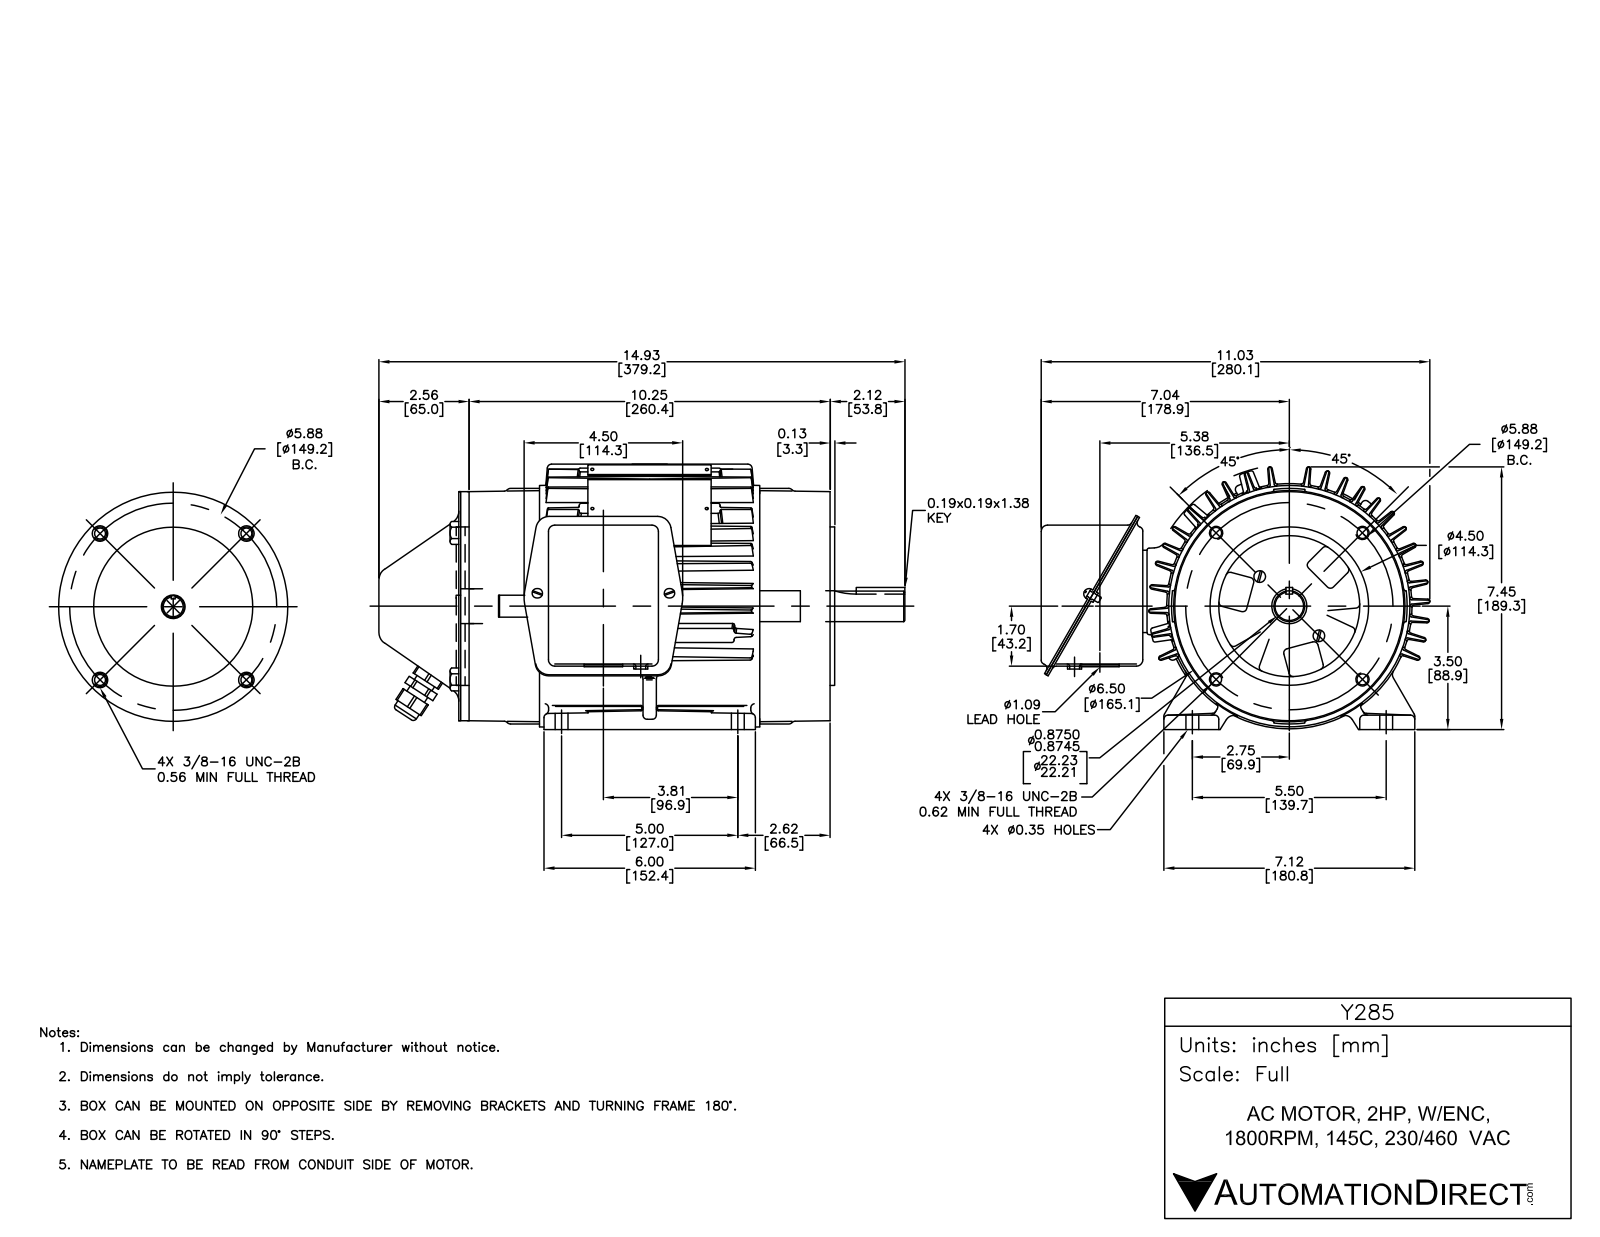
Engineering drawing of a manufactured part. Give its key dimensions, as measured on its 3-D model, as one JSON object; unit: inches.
{"part_name": "107387-625_Rev00 r1 w Y540 elec box r1", "step_written_by": "SolidWorks 2017 (AUTOMOTIVE_DESIGN)", "units": "inches", "bodies": {"solids": 32, "faces": 3253, "planar": 683, "cylindrical": 676, "other": 1894}, "overall_size": [14.679, 10.953, 7.437], "volume_in3": 134, "surface_area_in2": 1180, "round_holes": [[0.25, 8], [0.313, 8], [0.218, 6], [0.19, 5], [0.086, 4], [0.159, 4], [0.343, 4], [0.368, 4], [0.406, 4], [0.176, 2], [0.201, 2], [0.219, 2]], "round_bosses_or_shafts": [[0.399, 6], [0.5, 4], [0.19, 4], [0.166, 4], [0.375, 3], [0.313, 2], [0.295, 2], [0.187, 2]], "partial_cylinders_radius": [[0.06, 127], [0.12, 98], [0.38, 16], [0.06, 9], [0.18, 9], [0.156, 8], [0.16, 8], [0.035, 4]], "face_to_face_distances": [0.06, 10.25, 0.12, 0.25, 2.74, 3.06, 0.048, 2, 8.25, 10.13], "hole_center_spacings": [2.285, 5.513, 1.25, 1.768, 2.345, 2.937, 3.03, 3.169]}
